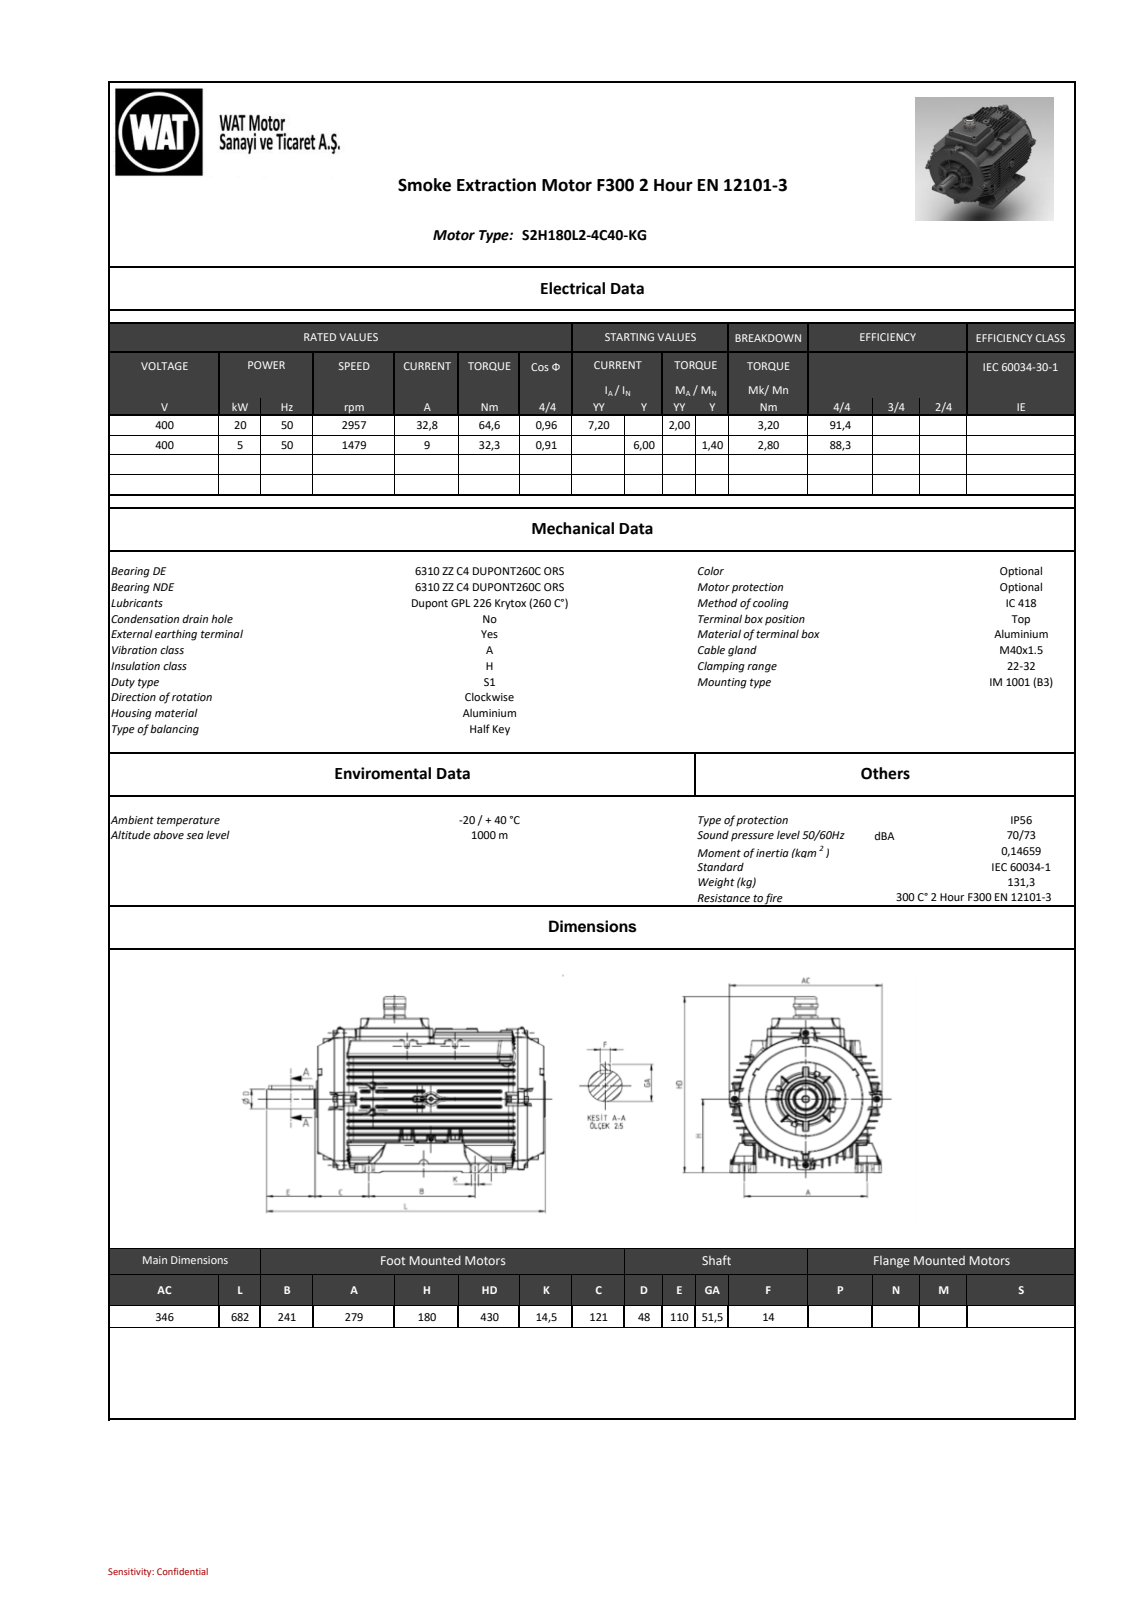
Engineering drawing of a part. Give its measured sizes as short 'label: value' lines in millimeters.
name: 001_objects
written by: SIEMENS PLM Software NX2206.8101 (AP203_CONFIGURATION_CONTROLLED_3D_DESIGN_OF_MECHANICAL_PARTS_AND_ASSEMBLIES_MIM_LF)
unit: mm
bodies: 0 solids, 7239 faces (1515 planar, 2282 cylindrical, 3442 other)
size: 682.5 × 431 × 346
holes: 4× ⌀5.6, 1× ⌀14, 1× ⌀17, 1× ⌀32, 1× ⌀62, 1× ⌀75.8, 1× ⌀76, 1× ⌀80
bosses: 4× ⌀12.73, 4× ⌀12, 3× ⌀8, 2× ⌀20, 1× ⌀303, 1× ⌀50, 1× ⌀49.5, 1× ⌀48
rounds: 668× R1, 652× R2, 82× R0.5, 66× R5, 26× R1.5, 10× R0.75, 10× R0.97, 9× R4
face distances: 16.21, 32.48, 16.27, 171.05, 173.83, 141.35, 157.62, 157.07, 140.86, 124.59
